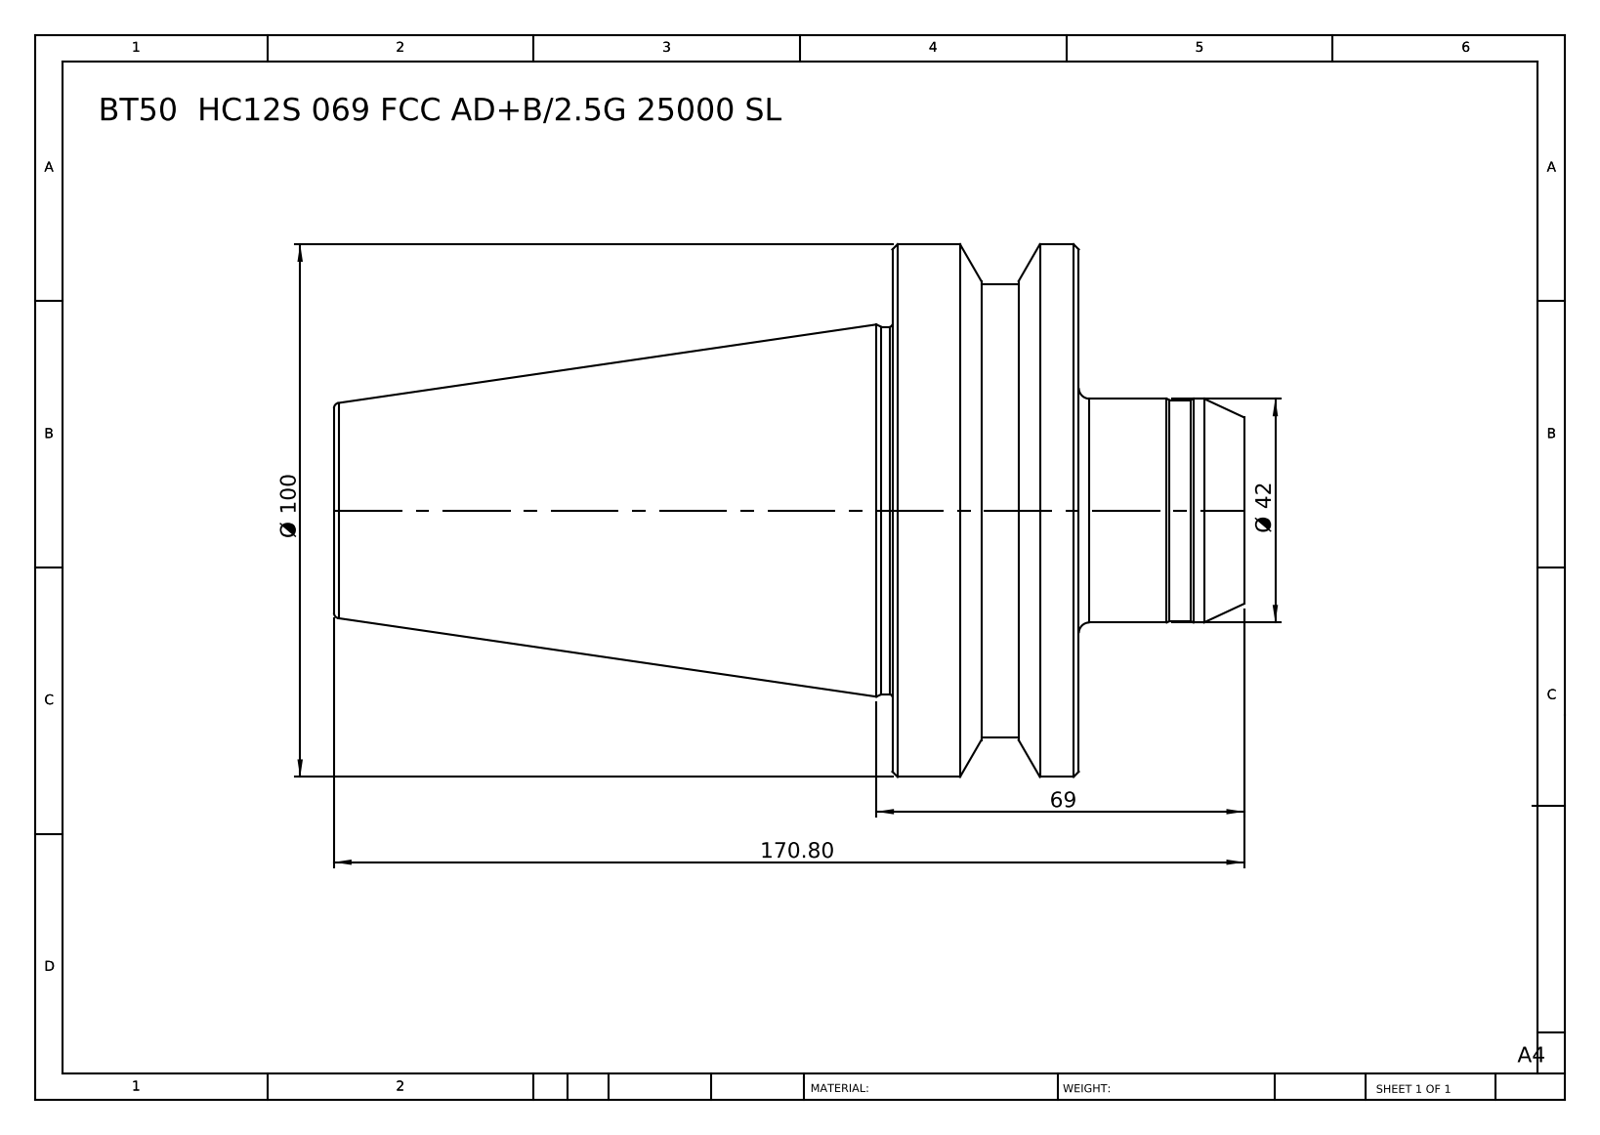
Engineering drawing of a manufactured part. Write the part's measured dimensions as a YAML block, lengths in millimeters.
part_name: "BT50 HC12S 069 FCC AD+B-2.5G 25000 SL"
step_written_by: "SolidWorks 2014 (CONFIG_CONTROL_DESIGN)"
units: millimeters
bodies: {solids: 1, faces: 44, planar: 6, cylindrical: 14, other: 24}
overall_size: [170.8, 100, 100]
volume: 551320
surface_area: 47941
round_bosses_or_shafts:
  - {diameter: 100, count: 1}
  - {diameter: 85, count: 1}
  - {diameter: 69, count: 1}
  - {diameter: 42, count: 1}
  - {diameter: 41.5, count: 1}
face_to_face_distances: [35, 139.8, 104.8, 31, 66, 170.8, 49.3, 18.3, 16.7, 121.5]
